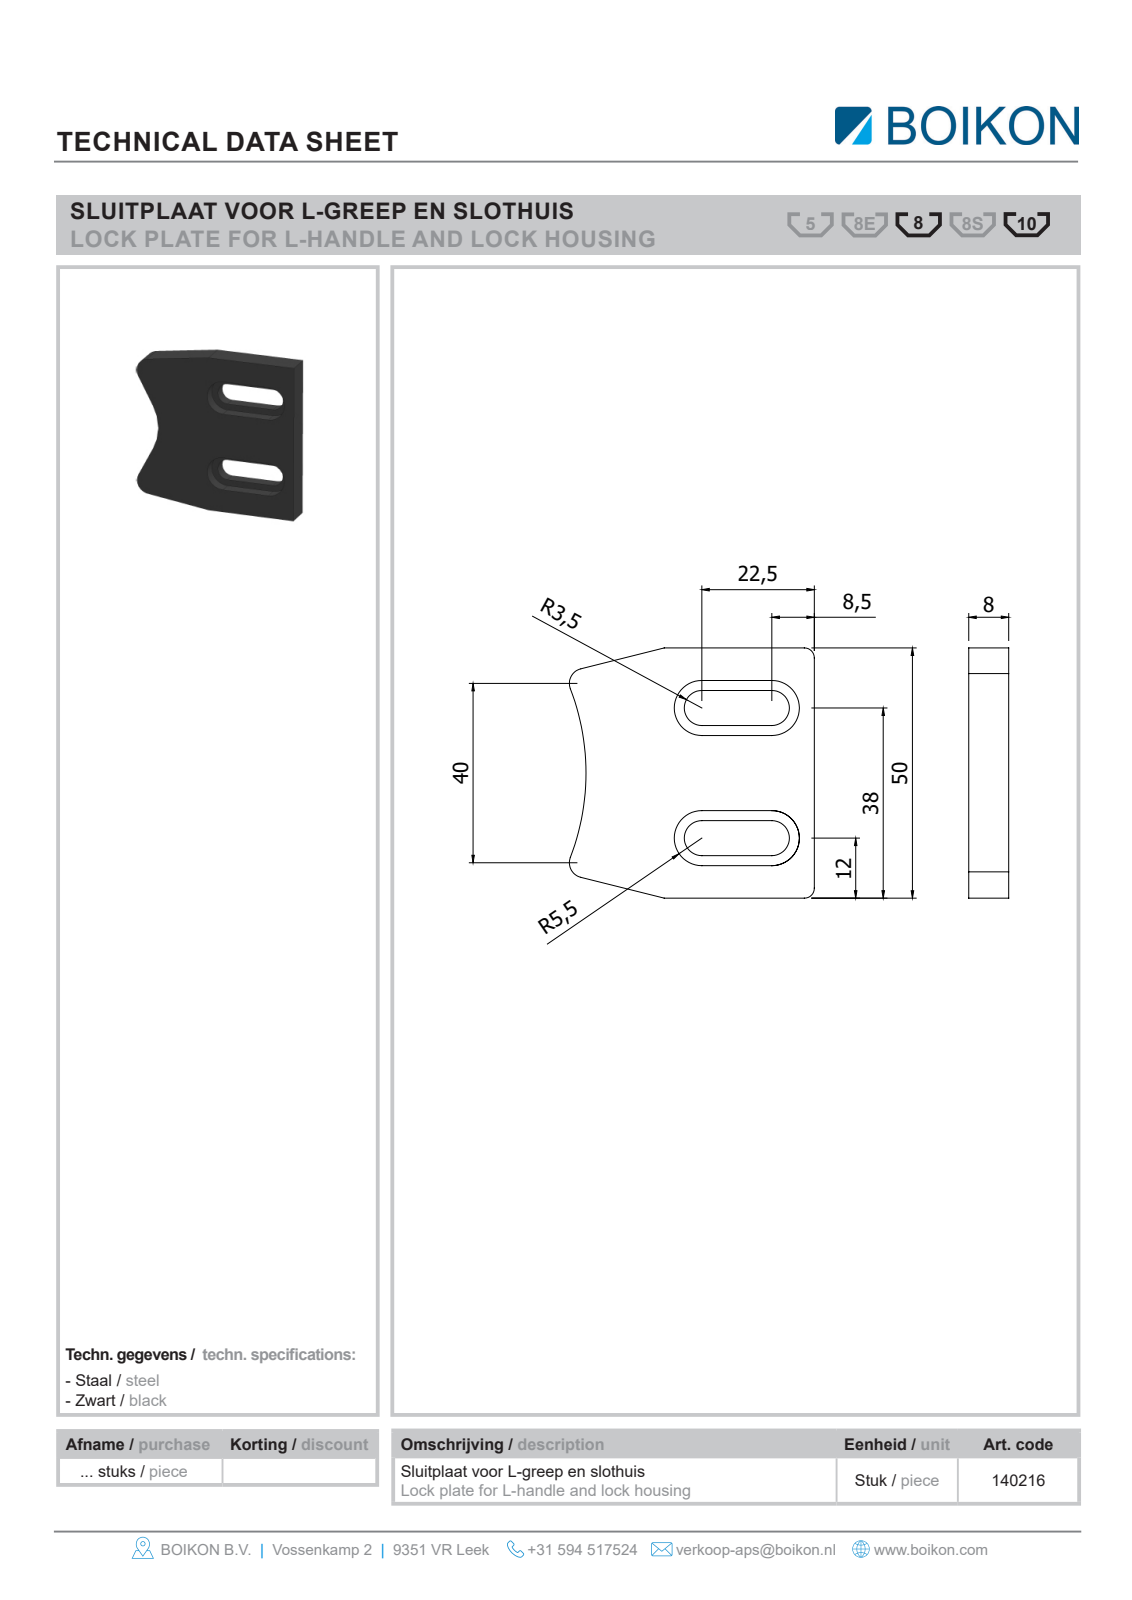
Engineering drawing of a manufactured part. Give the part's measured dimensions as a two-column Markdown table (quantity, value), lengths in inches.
| quantity | value |
| --- | --- |
| part name | Root; 140216SluitplaatBOIKON |
| STEP written by | HiCAD 2013 1802.4 Build 509 (AUTOMOTIVE_DESIGN) |
| units | inches |
| bodies | 1 solid, 30 faces (19 planar, 11 cylindrical, 0 other) |
| overall size | 2.039 × 1.969 × 0.315 |
| volume | 0.968 in³ |
| surface area | 10.36 in² |
| partial cylindrical surfaces (radius × count) | 0.128 × 4, 0.207 × 4, 0.157 × 2, 0.591 × 1 |
| main face-to-face distances | 0.315, 0.157, 0.079, 0.335, 0.984, 1.969, 0.699, 1.27, 0.62, 1.348 |
